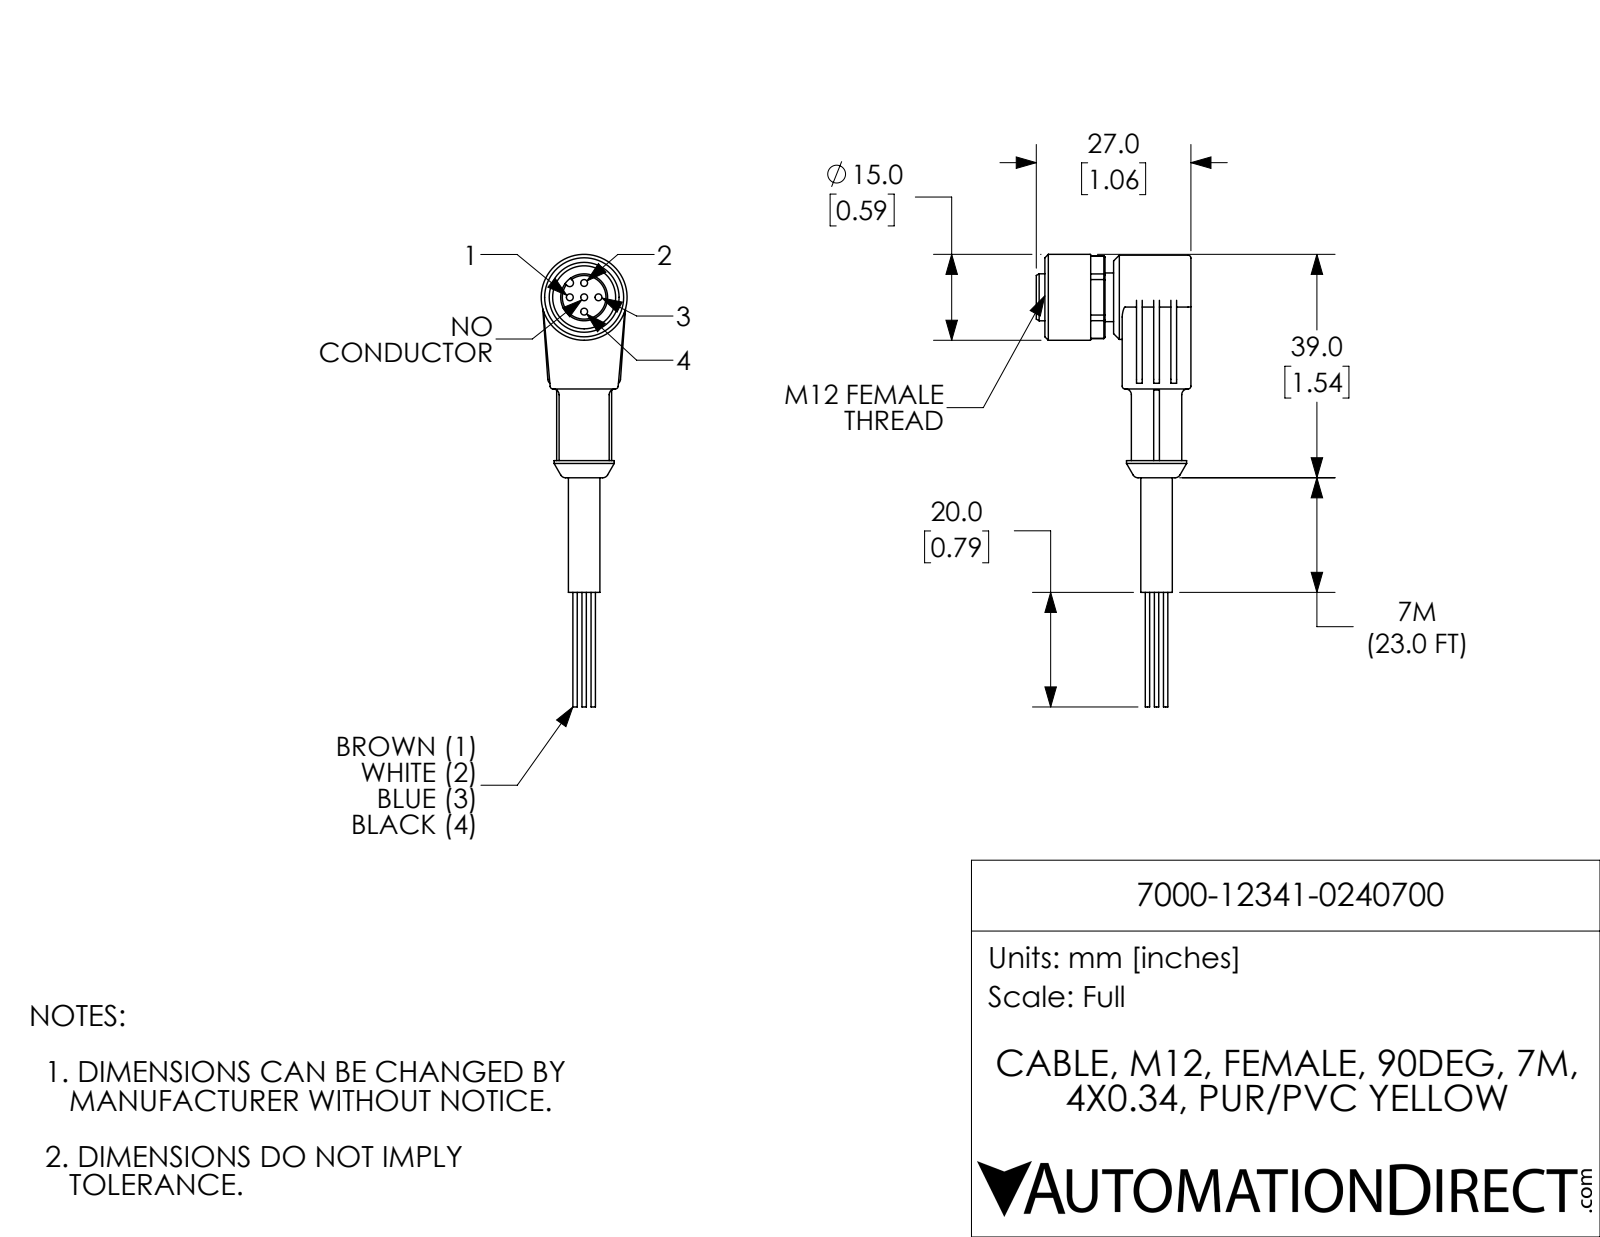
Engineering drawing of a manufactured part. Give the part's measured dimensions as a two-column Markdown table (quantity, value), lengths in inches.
| quantity | value |
| --- | --- |
| part name | 7000-12341-0240700 |
| STEP written by | SolidWorks 2017 (AUTOMOTIVE_DESIGN) |
| units | inches |
| bodies | 1 solid, 152 faces (65 planar, 59 cylindrical, 28 other) |
| overall size | 3.11 × 1.063 × 0.591 |
| volume | 0.417 in³ |
| surface area | 5.896 in² |
| round holes (diameter × count) | 0.047 × 5, 0.189 × 1, 0.433 × 1 |
| round bosses / shafts (diameter × count) | 0.03 × 4, 0.591 × 1, 0.579 × 1, 0.413 × 1, 0.346 × 1, 0.335 × 1, 0.323 × 1, 0.217 × 1 |
| partial cylindrical surfaces (radius × count) | 0.02 × 8, 0.039 × 2, 0.026 × 1, 0.283 × 1 |
| main face-to-face distances | 0.472, 0.059, 0.118, 0.531, 0.591, 0.217, 0.374, 0.236, 0.315, 0.492 |
| hole center spacings | 0.098, 0.139, 0.197 |
